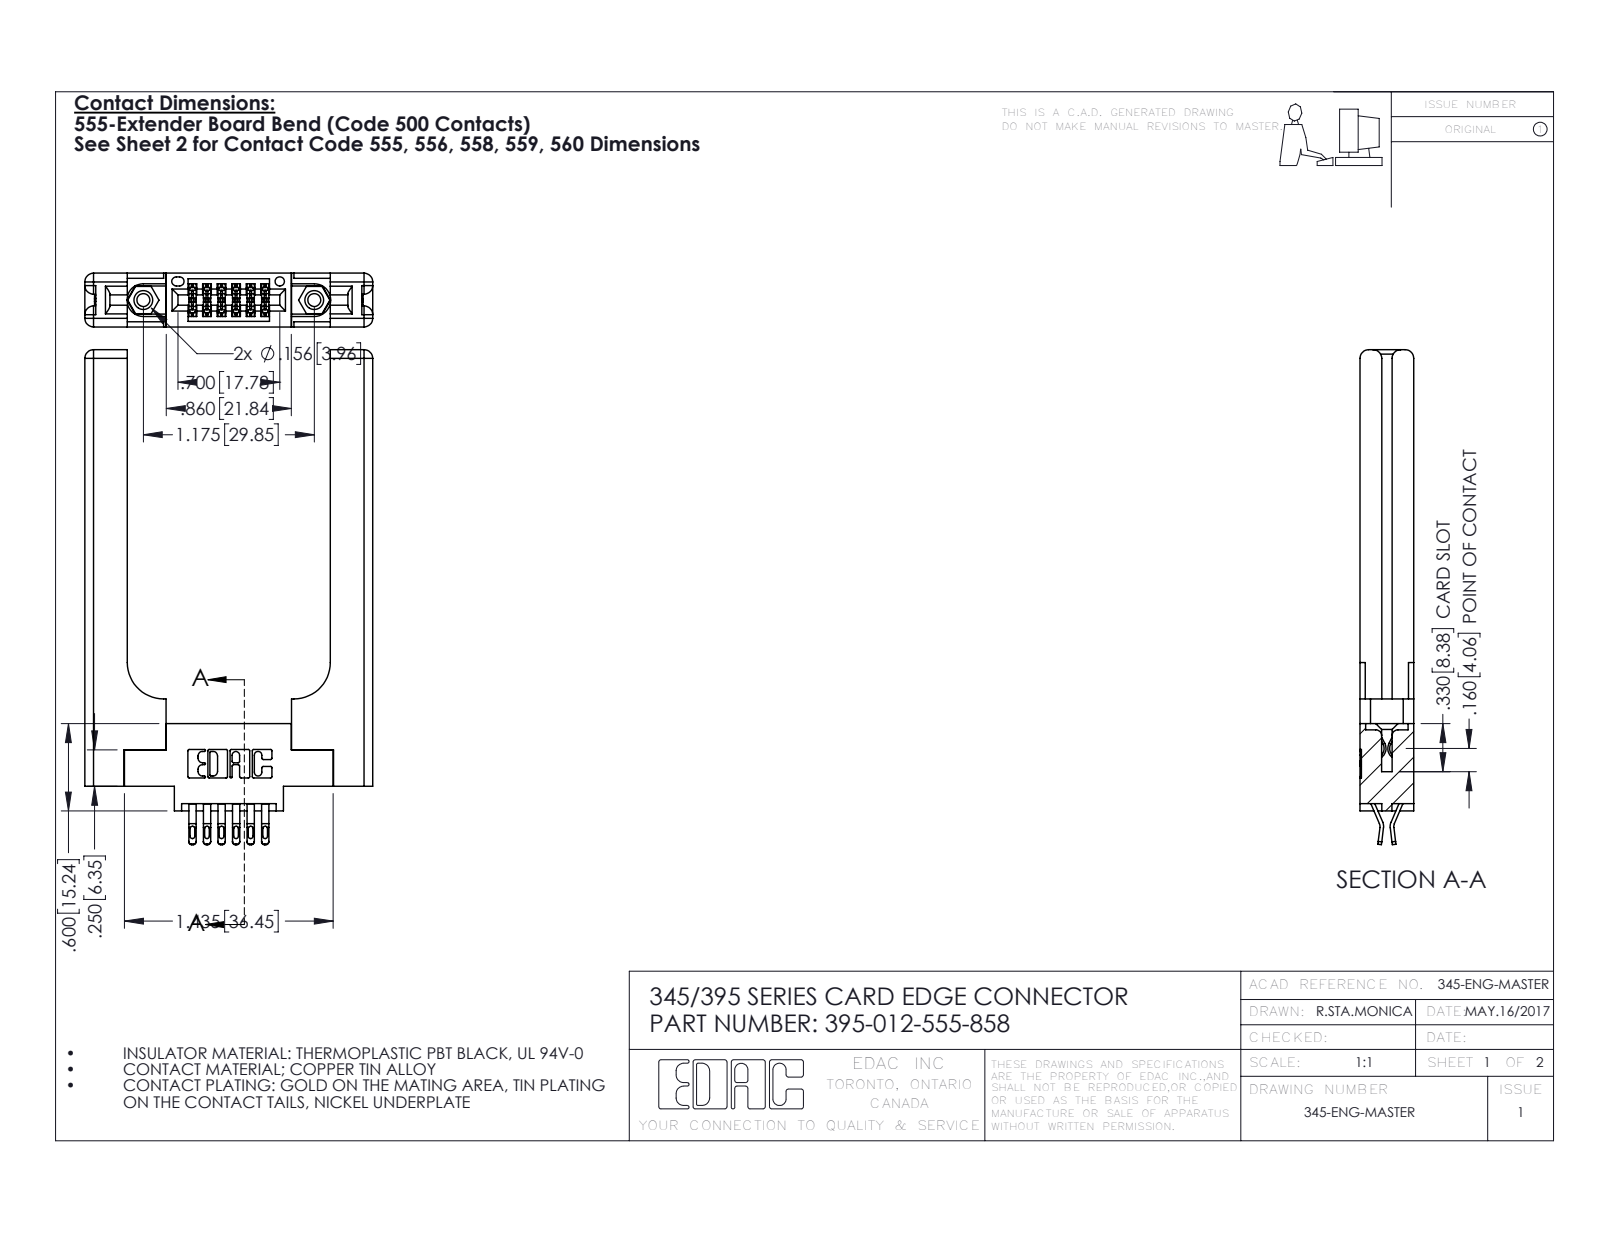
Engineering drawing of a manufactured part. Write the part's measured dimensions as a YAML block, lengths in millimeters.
part_name: "395-012-555-858; 345-292-001_555 Tail; 345-250-001_345-250-001-102; 345 Part_0.170 Offset - 0.156 Dia-TH (+1 more)"
step_written_by: "SolidWorks 2016 (CONFIG_CONTROL_DESIGN)"
units: millimeters
bodies: {solids: 17, faces: 1058, planar: 604, cylindrical: 394, other: 60}
overall_size: [86.4, 50.3, 9.4]
volume: 12900
surface_area: 11230
round_holes:
  - {diameter: 2.3, count: 2}
  - {diameter: 3.2, count: 2}
  - {diameter: 4, count: 2}
  - {diameter: 1.6, count: 1}
round_bosses_or_shafts:
  - {diameter: 3.9, count: 2}
partial_cylinders:
  - {radius: 0.4, count: 30}
  - {radius: 0.5, count: 24}
  - {radius: 0.3, count: 22}
  - {radius: 0.2, count: 18}
  - {radius: 1.5, count: 16}
  - {radius: 0.2, count: 6}
  - {radius: 0.8, count: 6}
  - {radius: 0.7, count: 3}
face_to_face_distances: [9.4, 3.8, 5.6, 1.8, 3.8, 2, 35.5, 7.6, 1.8, 7.4]
hole_center_spacings: [6.9, 24, 29.8]
